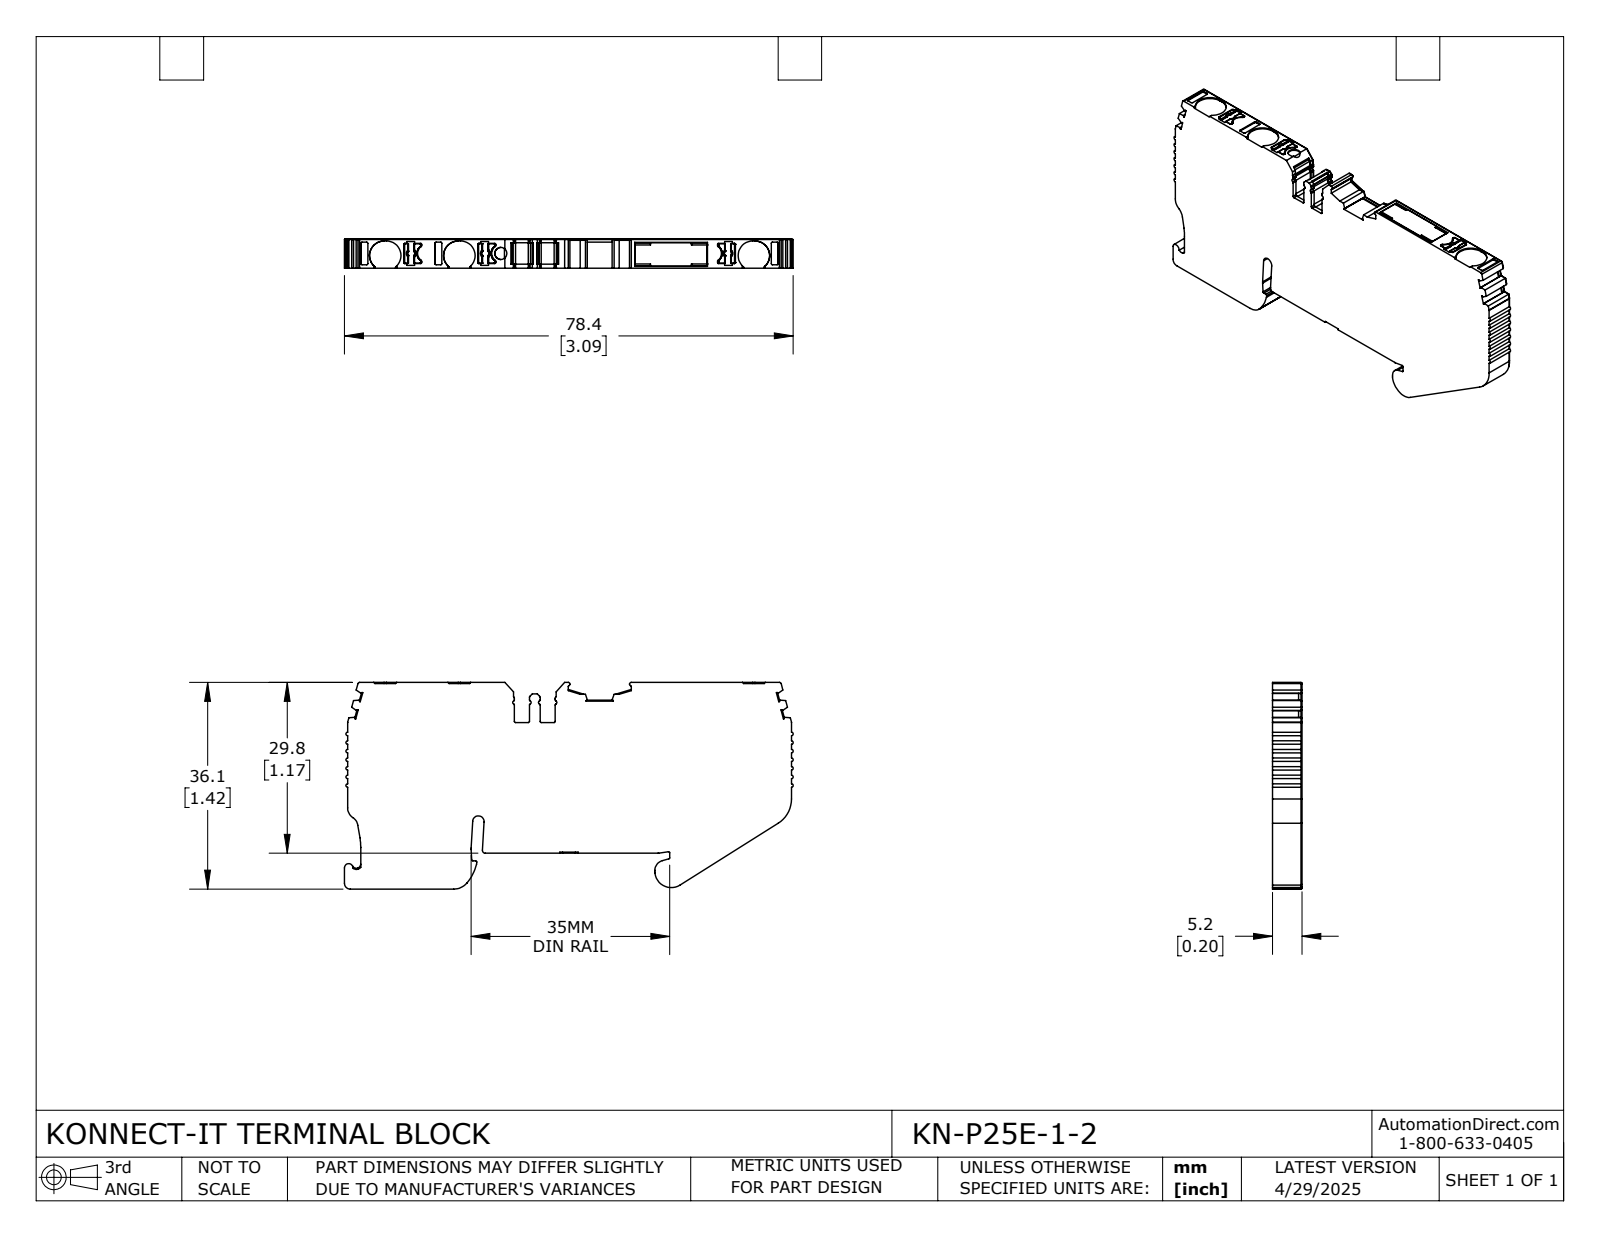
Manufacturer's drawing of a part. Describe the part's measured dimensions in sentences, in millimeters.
The part is named "KN-P25E-1-2". Its 3-D file was written by "SolidWorks 2024 (CONFIG_CONTROL_DESIGN)". It is 1 solid with 678 faces: 362 planar, 265 cylindrical and 51 other. Overall it measures 78.36 by 36.07 by 5.15 millimeters. Its volume is 11 978 cubic millimeters and its surface area 6 220 square millimeters. Round holes: 1 of diameter 2.1. Partial cylindrical surfaces (rounded edges, fillets, slot ends): 66 of radius 0.2, 39 of radius 0.3, 19 of radius 0.1, 18 of radius 0.5, 12 of radius 0.15, 9 of radius 0.4, 6 of radius 2.55, 3 of radius 1. The main face-to-face distances are 5.15, 29.81, 29.61, 6.26, 35.87, 36.07, 77.52, 1.2, 5, 4.5.
